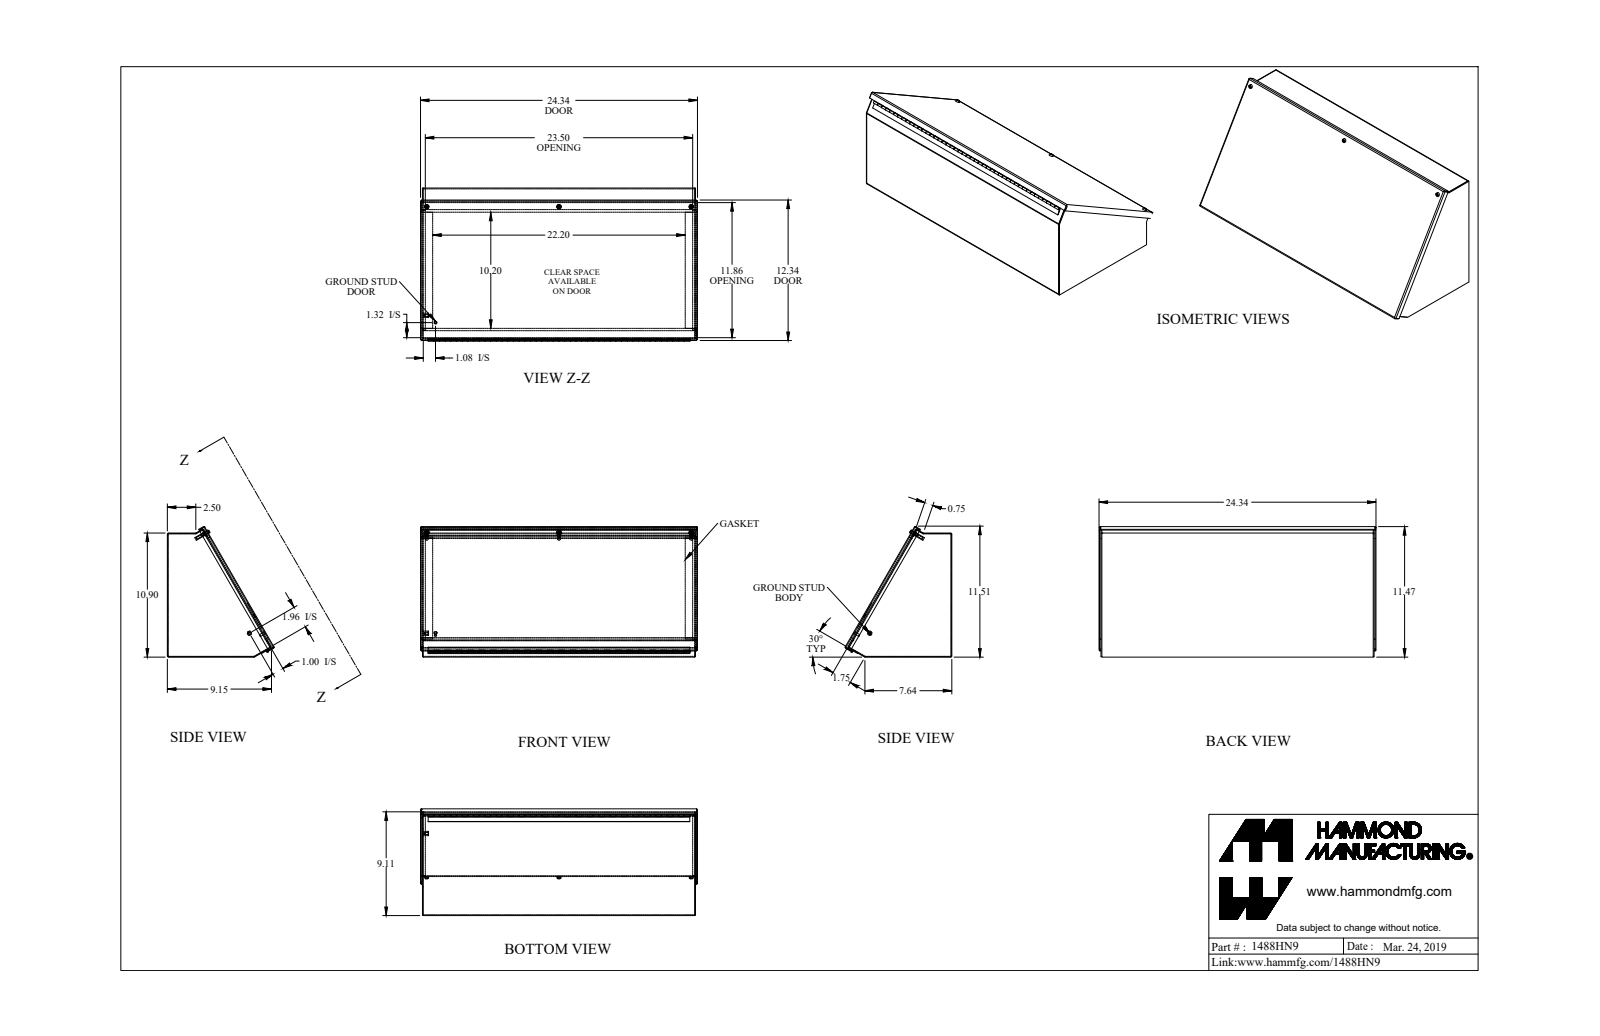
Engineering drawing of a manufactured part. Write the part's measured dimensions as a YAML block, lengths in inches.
part_name: "1488HN9_Default"
step_written_by: "SolidWorks 2019 (CONFIG_CONTROL_DESIGN)"
units: inches
bodies: {solids: 20, faces: 739, planar: 492, cylindrical: 215, other: 32}
overall_size: [24.343, 11.469, 9.374]
volume: 95.27
surface_area: 2389
round_holes:
  - {diameter: 0.159, count: 3}
  - {diameter: 0.25, count: 3}
  - {diameter: 0.156, count: 1}
round_bosses_or_shafts:
  - {diameter: 0.39, count: 3}
  - {diameter: 0.275, count: 3}
  - {diameter: 0.19, count: 3}
  - {diameter: 0.148, count: 3}
  - {diameter: 0.375, count: 1}
  - {diameter: 0.25, count: 1}
  - {diameter: 0.188, count: 1}
  - {diameter: 0.174, count: 1}
partial_cylinders:
  - {radius: 0.036, count: 12}
  - {radius: 0.108, count: 12}
  - {radius: 0.125, count: 3}
  - {radius: 0.16, count: 3}
  - {radius: 0.171, count: 3}
face_to_face_distances: [0.072, 23.928, 10.828, 23.856, 24, 0.072, 0.25, 0.125, 0.197, 10.9]
hole_center_spacings: [11.625, 11.625, 23.25, 23.25]
